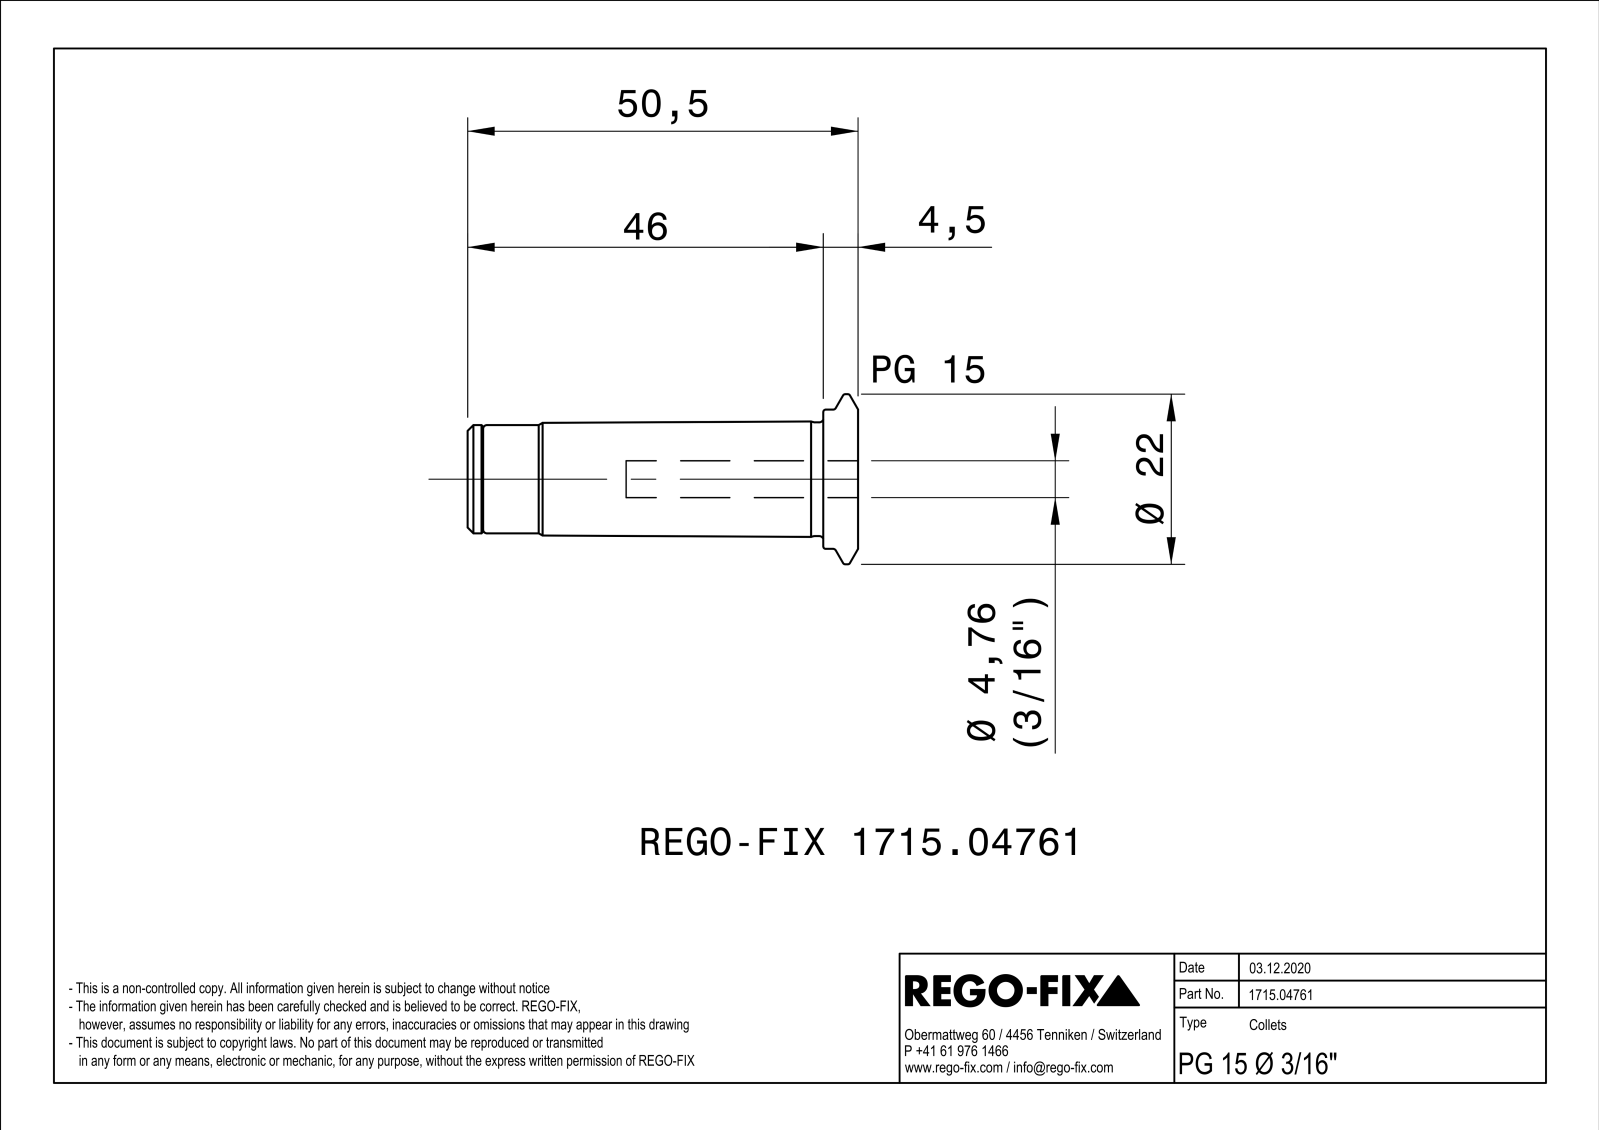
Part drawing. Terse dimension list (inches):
name: NOCUT
written by: SIEMENS PLM Software Solid Edge ST10 (AUTOMOTIVE_DESIGN)
unit: in
bodies: 0 solids, 117 faces (35 planar, 32 cylindrical, 50 other)
size: 1.988 × 0.866 × 0.866
holes: 1× ⌀0.187, 1× ⌀0.205, 1× ⌀0.272, 1× ⌀0.323, 1× ⌀0.335, 1× ⌀0.43, 1× ⌀0.48
bosses: 1× ⌀0.866, 1× ⌀0.709, 1× ⌀0.579, 1× ⌀0.551
rounds: 6× R0.02, 1× R0.205, 1× R0.236
face distances: 0.039, 0.079, 1.988, 1.594, 0.394, 1.634, 0.354, 0.118, 0.177, 1.417
